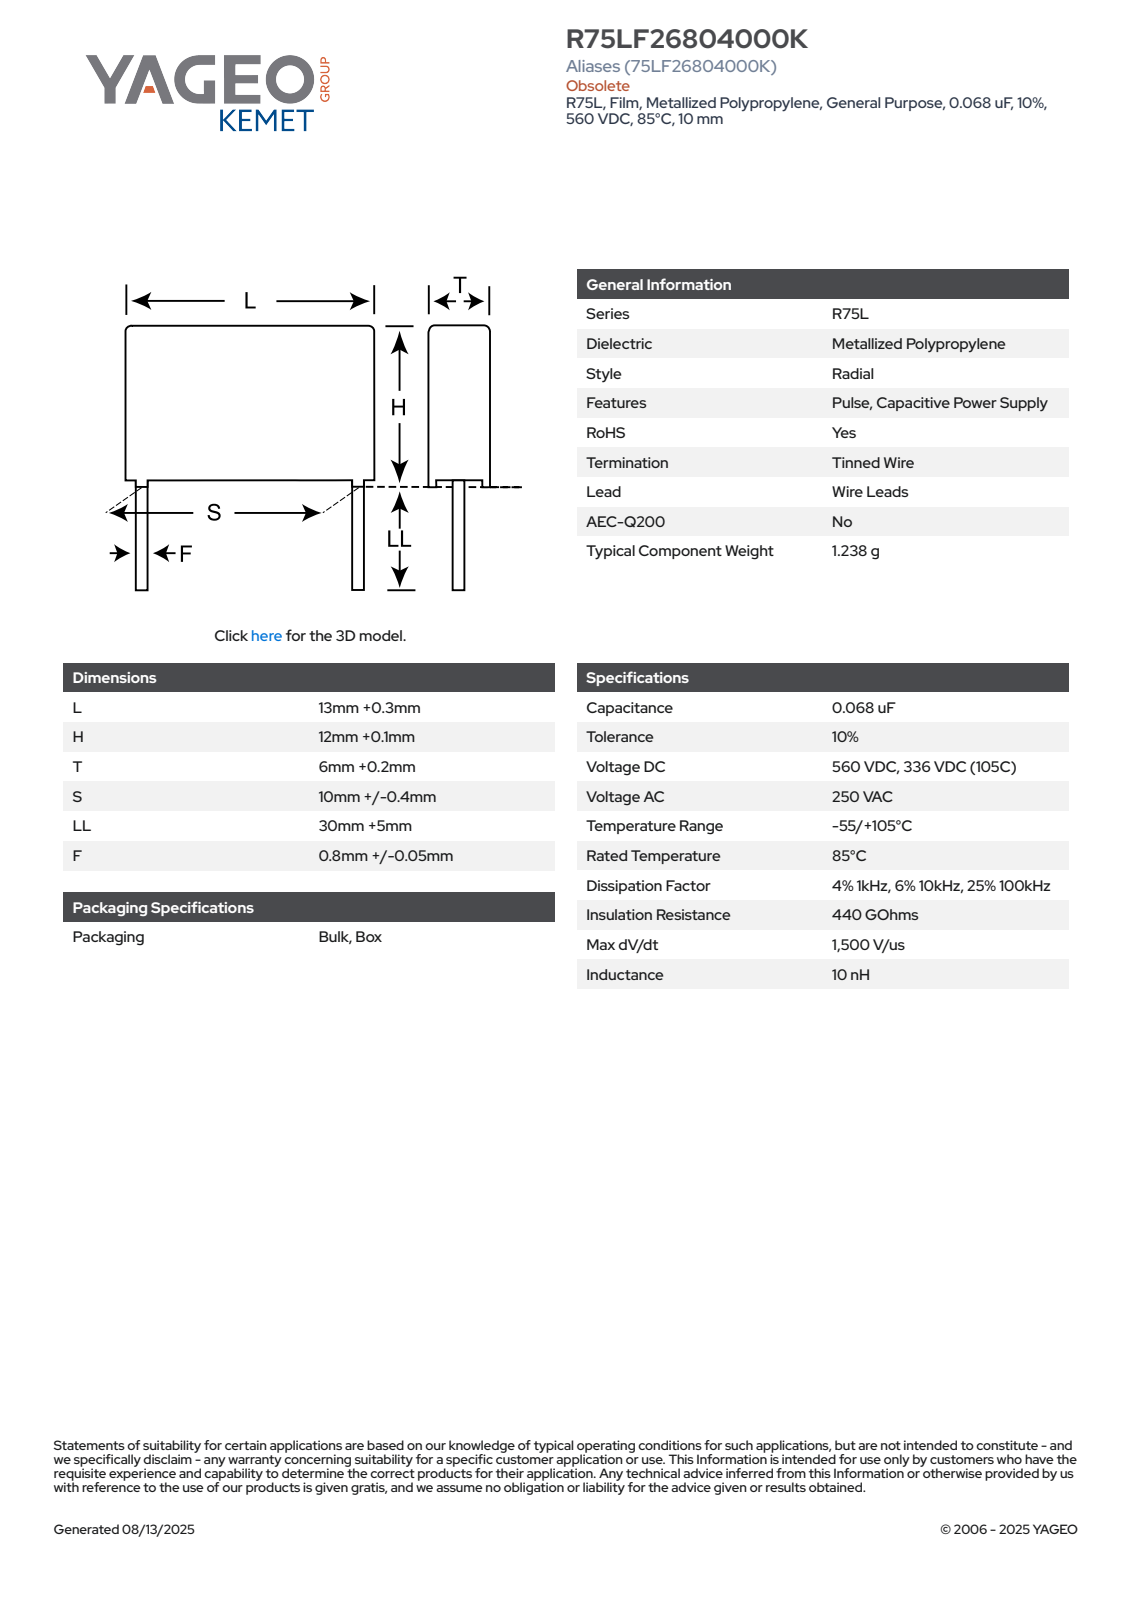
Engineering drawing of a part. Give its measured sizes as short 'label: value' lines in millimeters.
name: CFR_RB3_13X12X6_L13.3H12.1T6.2S10LL35F0.85
written by: SolidWorks 2014 (AUTOMOTIVE_DESIGN)
unit: mm
bodies: 4 solids, 85 faces (77 planar, 8 cylindrical, 0 other)
size: 47.1 × 13.3 × 6.21
volume: 984 mm³; area: 848 mm²
bosses: 2× ⌀0.85
rounds: 4× R0.5
face distances: 6.2, 13.3, 11.35, 0.44, 5.76, 0.75, 12.1, 12.86, 5.32, 0.42
